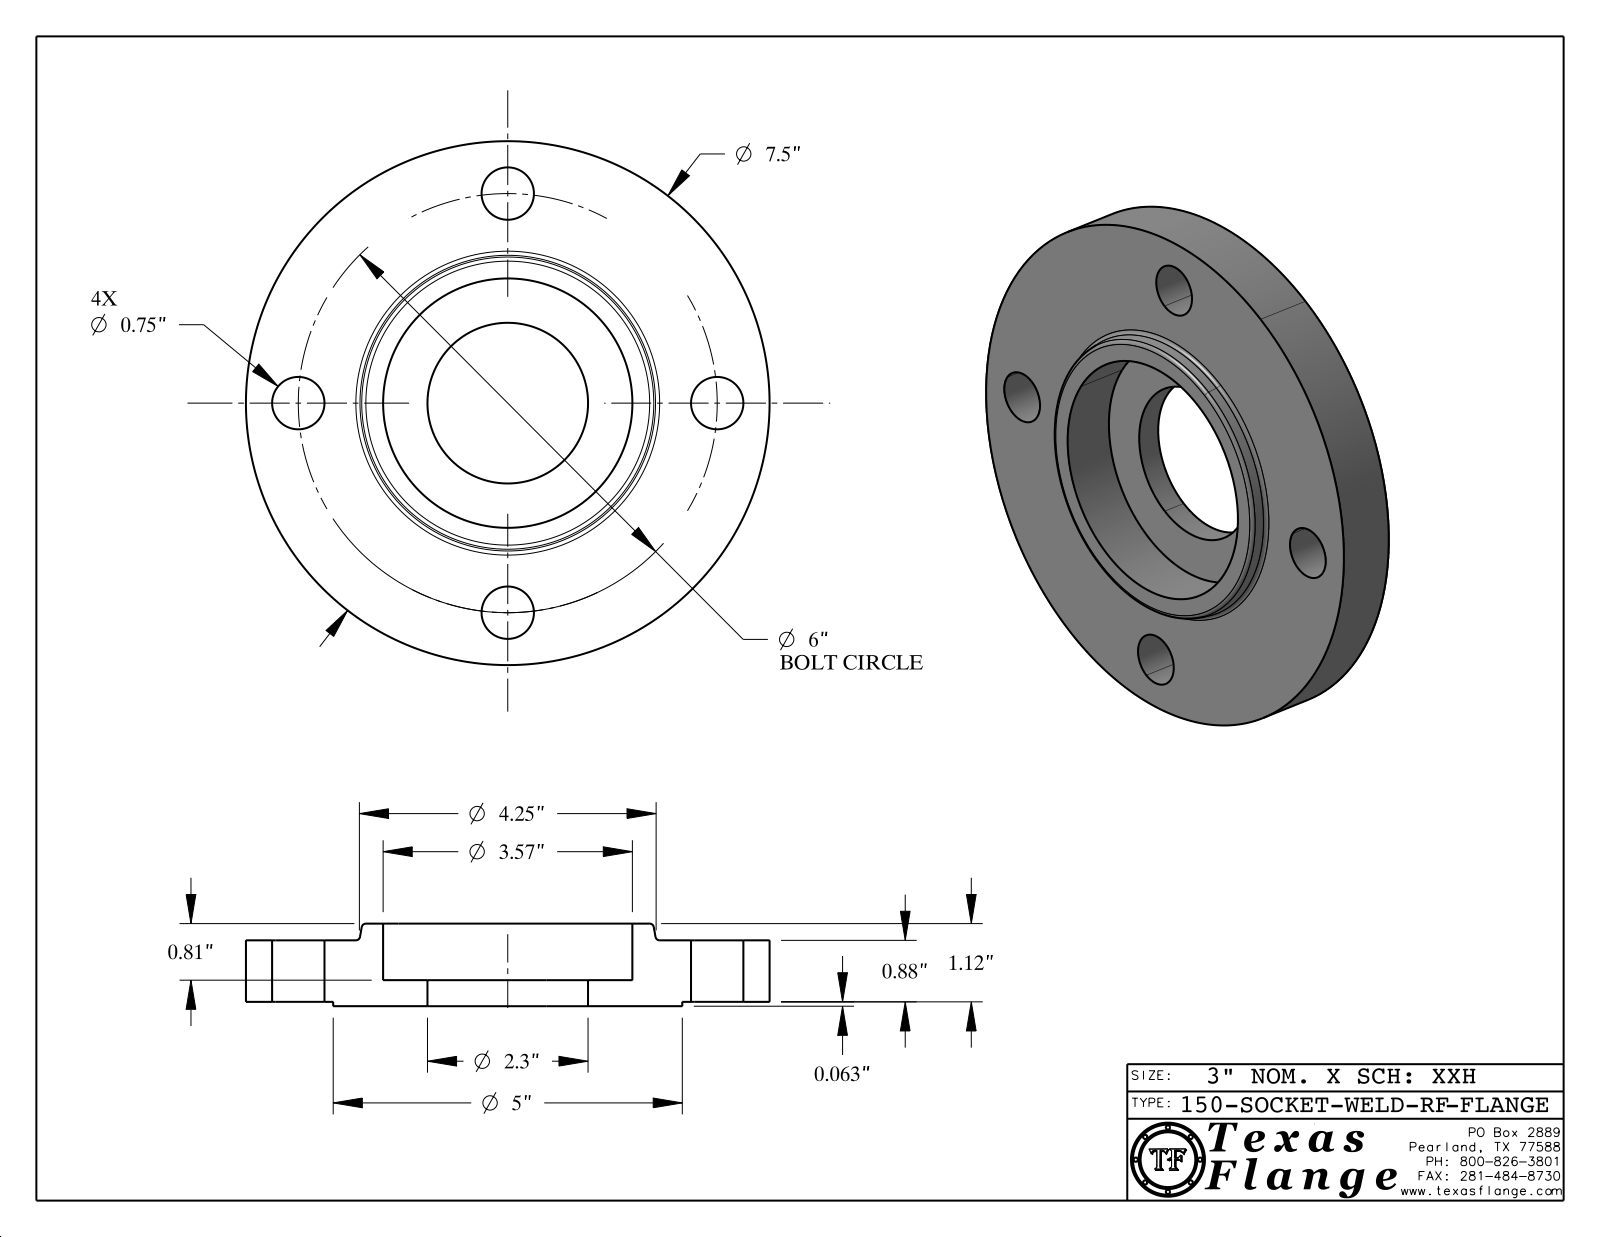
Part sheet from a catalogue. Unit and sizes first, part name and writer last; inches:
Units: inches
Overall size (bounding box): 7.5 × 7.5 × 1.183
Round holes (diameter × count): ⌀0.75 ×4, ⌀0.495 ×1, ⌀2.3 ×1, ⌀3.57 ×1
Round bosses / shafts (diameter × count): ⌀0.03 ×8, ⌀7.5 ×1, ⌀5 ×1, ⌀0.39 ×1
Main face-to-face distances: 0.88, 0.063, 0.943, 0.372, 0.31, 0.57, 1.183, 1.12, 0.81, 0.24
Hole centre spacings: 3, 4.243, 2.296, 5.543, 6
Volume: 32.23 in³ · Surface area: 120.6 in²
Bodies: 1 solid, 412 faces (370 planar, 36 cylindrical, 6 other)
Part name (STEP PRODUCT): 150-SOCKET-WELD-RF
STEP written by: CATIA V5 STEP AP214 (AUTOMOTIVE_DESIGN)
